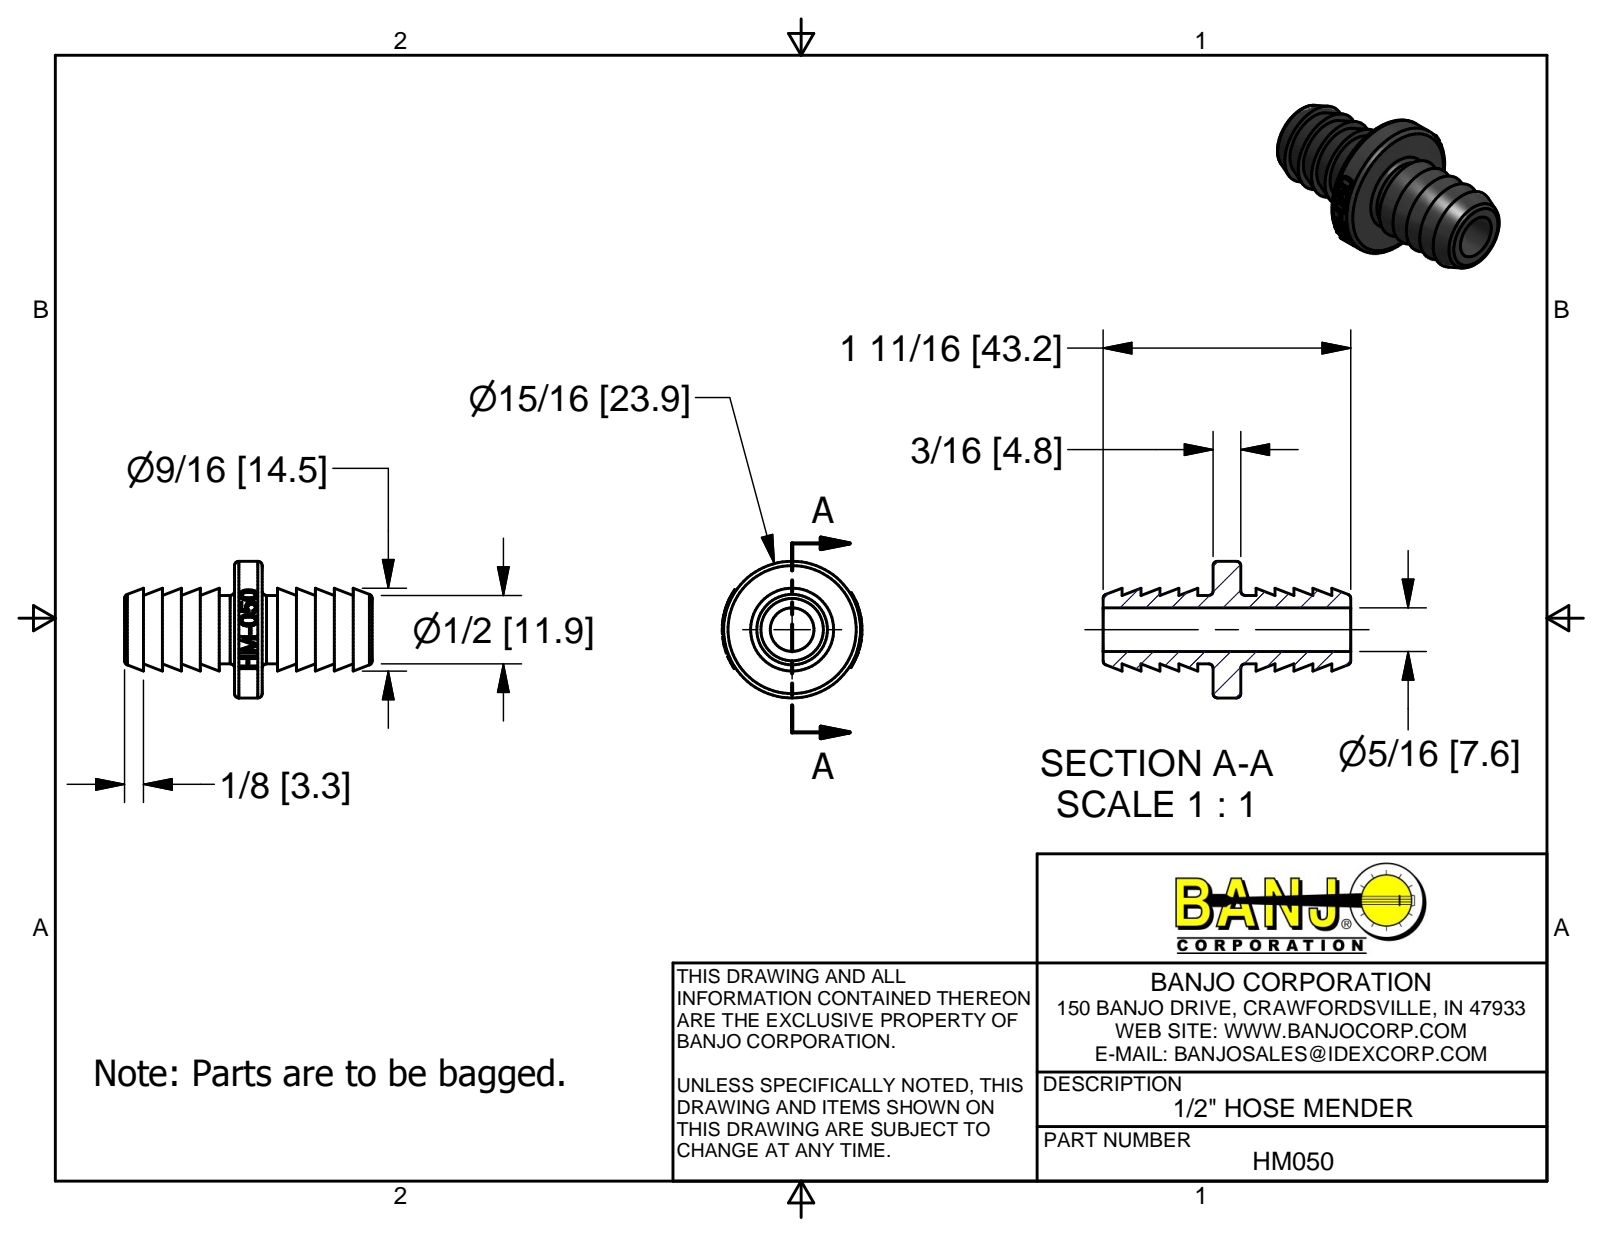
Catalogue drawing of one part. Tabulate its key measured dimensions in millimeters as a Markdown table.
| quantity | value |
| --- | --- |
| part name | HM050 |
| STEP written by | Autodesk Inventor 2014 (AUTOMOTIVE_DESIGN) |
| units | millimeters |
| bodies | 1 solid, 180 faces (72 planar, 21 cylindrical, 87 other) |
| overall size | 43.18 × 24.38 × 23.88 |
| volume | 5 322 mm³ |
| surface area | 4 354 mm² |
| round holes (diameter × count) | 7.62 × 1 |
| round bosses / shafts (diameter × count) | 23.88 × 1, 11.94 × 1 |
| partial cylindrical surfaces (radius × count) | 12.19 × 1 |
| main face-to-face distances | 3.3, 26.67, 4.83, 23.37, 6.6, 6.61, 9.91, 13.21, 29.97, 3.31 |
